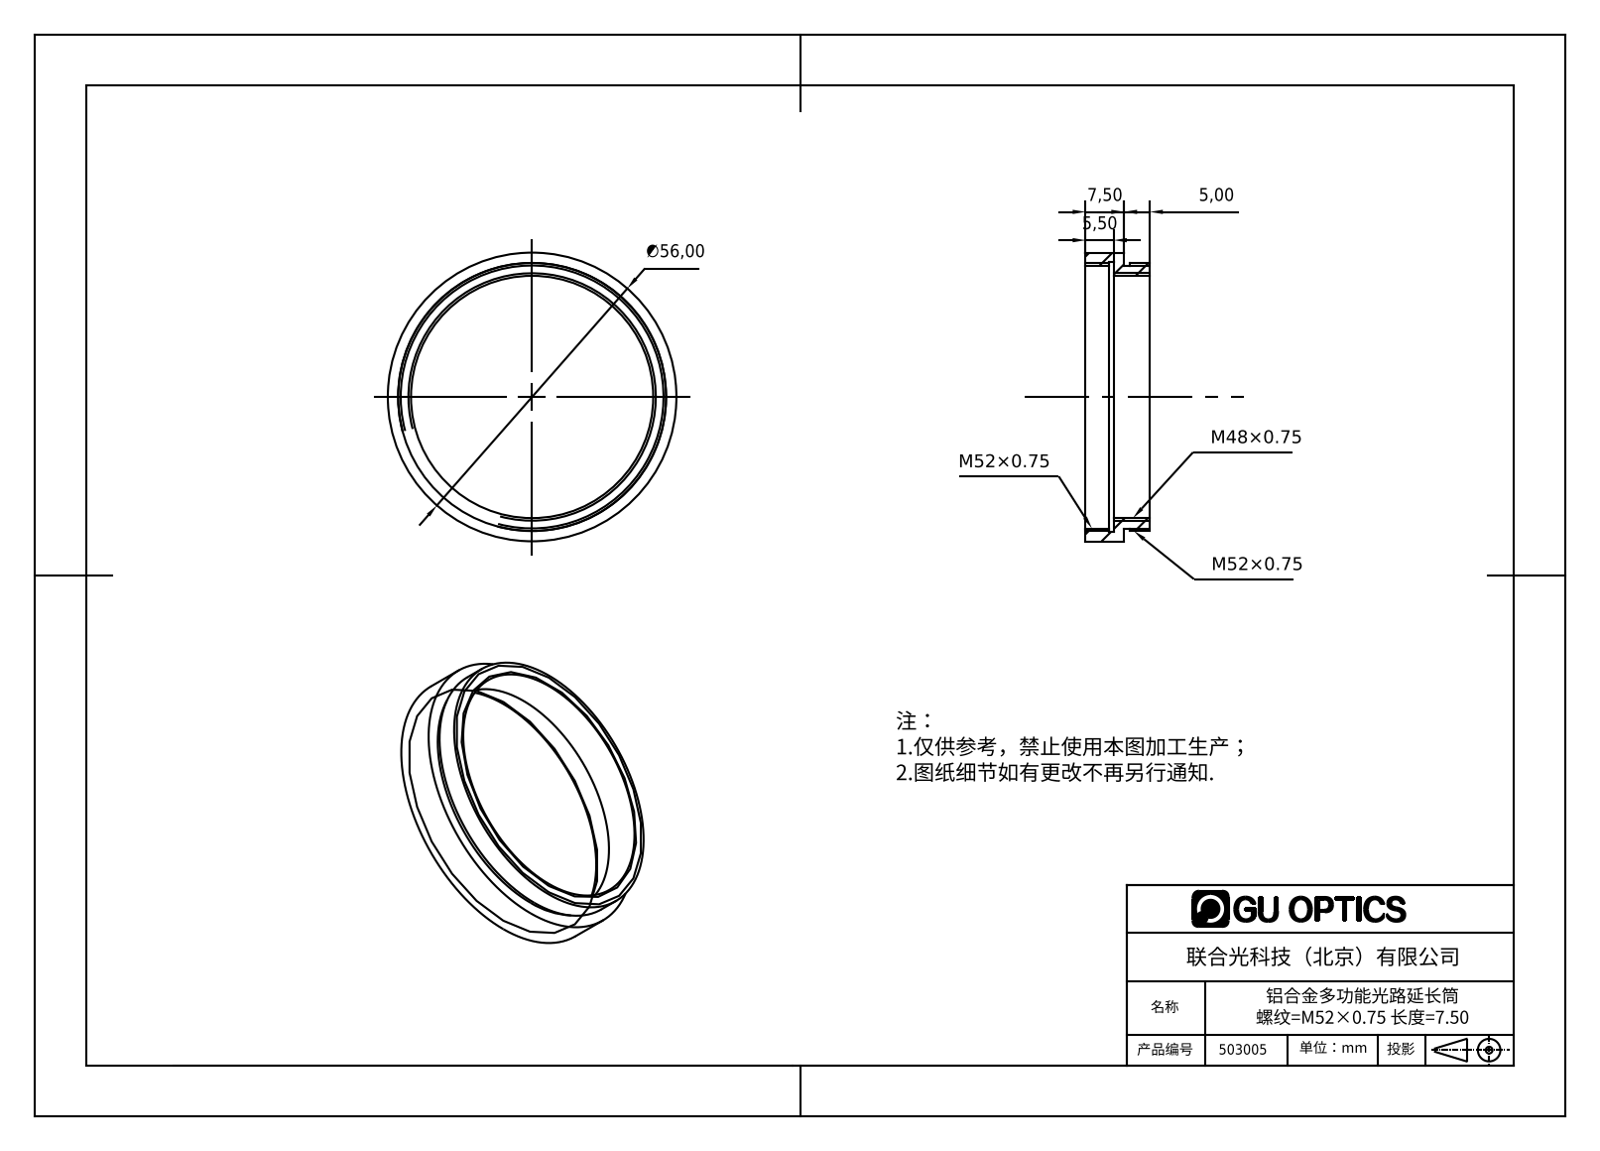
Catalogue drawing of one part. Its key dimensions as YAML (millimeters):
part_name: "503005"
step_written_by: "SolidWorks 2016 (AUTOMOTIVE_DESIGN)"
units: millimeters
bodies: {solids: 1, faces: 18, planar: 6, cylindrical: 12, other: 0}
overall_size: [56, 56, 12.5]
volume: 5533
surface_area: 5864
round_holes:
  - {diameter: 47, count: 1}
  - {diameter: 51, count: 1}
  - {diameter: 52.2, count: 1}
round_bosses_or_shafts:
  - {diameter: 56, count: 1}
  - {diameter: 52, count: 1}
face_to_face_distances: [7.5, 5.5, 2, 12.5, 7, 5, 1, 3, 4, 4.5]
